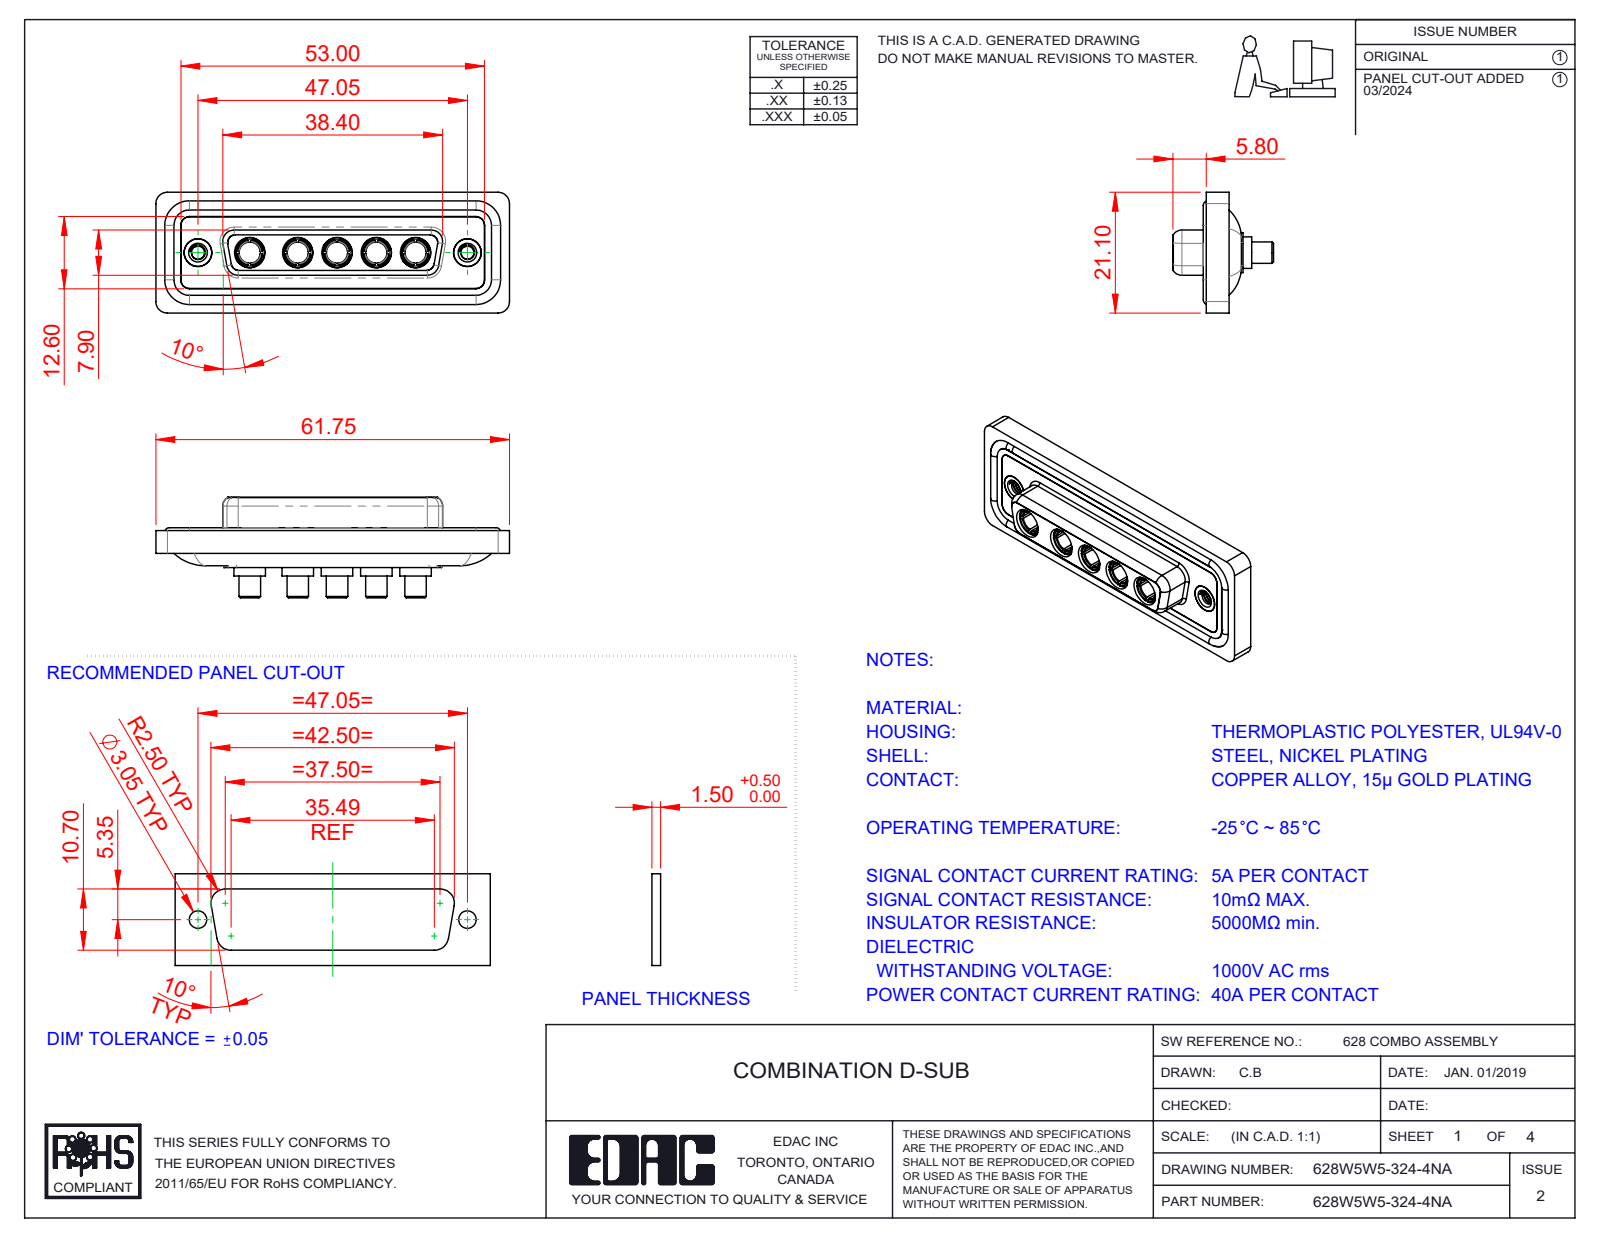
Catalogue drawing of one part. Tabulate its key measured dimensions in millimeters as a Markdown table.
| quantity | value |
| --- | --- |
| part name | 628Combo Housing_5W5; 628Combo Shell Front_25 Contacts; 628Combo Shell Rear_25 Contacts; Power Socket_40A S (+3 more) |
| STEP written by | SolidWorks 2023 (CONFIG_CONTROL_DESIGN) |
| units | millimeters |
| bodies | 17 solids, 754 faces (250 planar, 305 cylindrical, 199 other) |
| overall size | 61.75 × 21.1 × 17.55 |
| volume | 8 267 mm³ |
| surface area | 13 467 mm² |
| round holes (diameter × count) | 4.85 × 7, 3.7 × 5, 5.3 × 5, 2.26 × 2, 4 × 2, 4.05 × 2, 5 × 2 |
| round bosses / shafts (diameter × count) | 5.5 × 5, 5.2 × 5, 4.96 × 5, 4.75 × 5, 3.75 × 5, 1.6 × 4, 4.95 × 2, 4.8 × 2 |
| partial cylindrical surfaces (radius × count) | 1.5 × 22, 2 × 18, 1.35 × 8, 1.6 × 8, 2.1 × 5, 0.25 × 4, 0.5 × 4, 0.6 × 4 |
| main face-to-face distances | 0.4, 1.8, 7.45, 5.65, 0.5, 7.05, 6.6, 1.6, 1.1, 2.9 |
| hole center spacings | 6.86, 9.04, 13.72, 38.01, 8.39, 15.25, 15.9, 17.43 |
